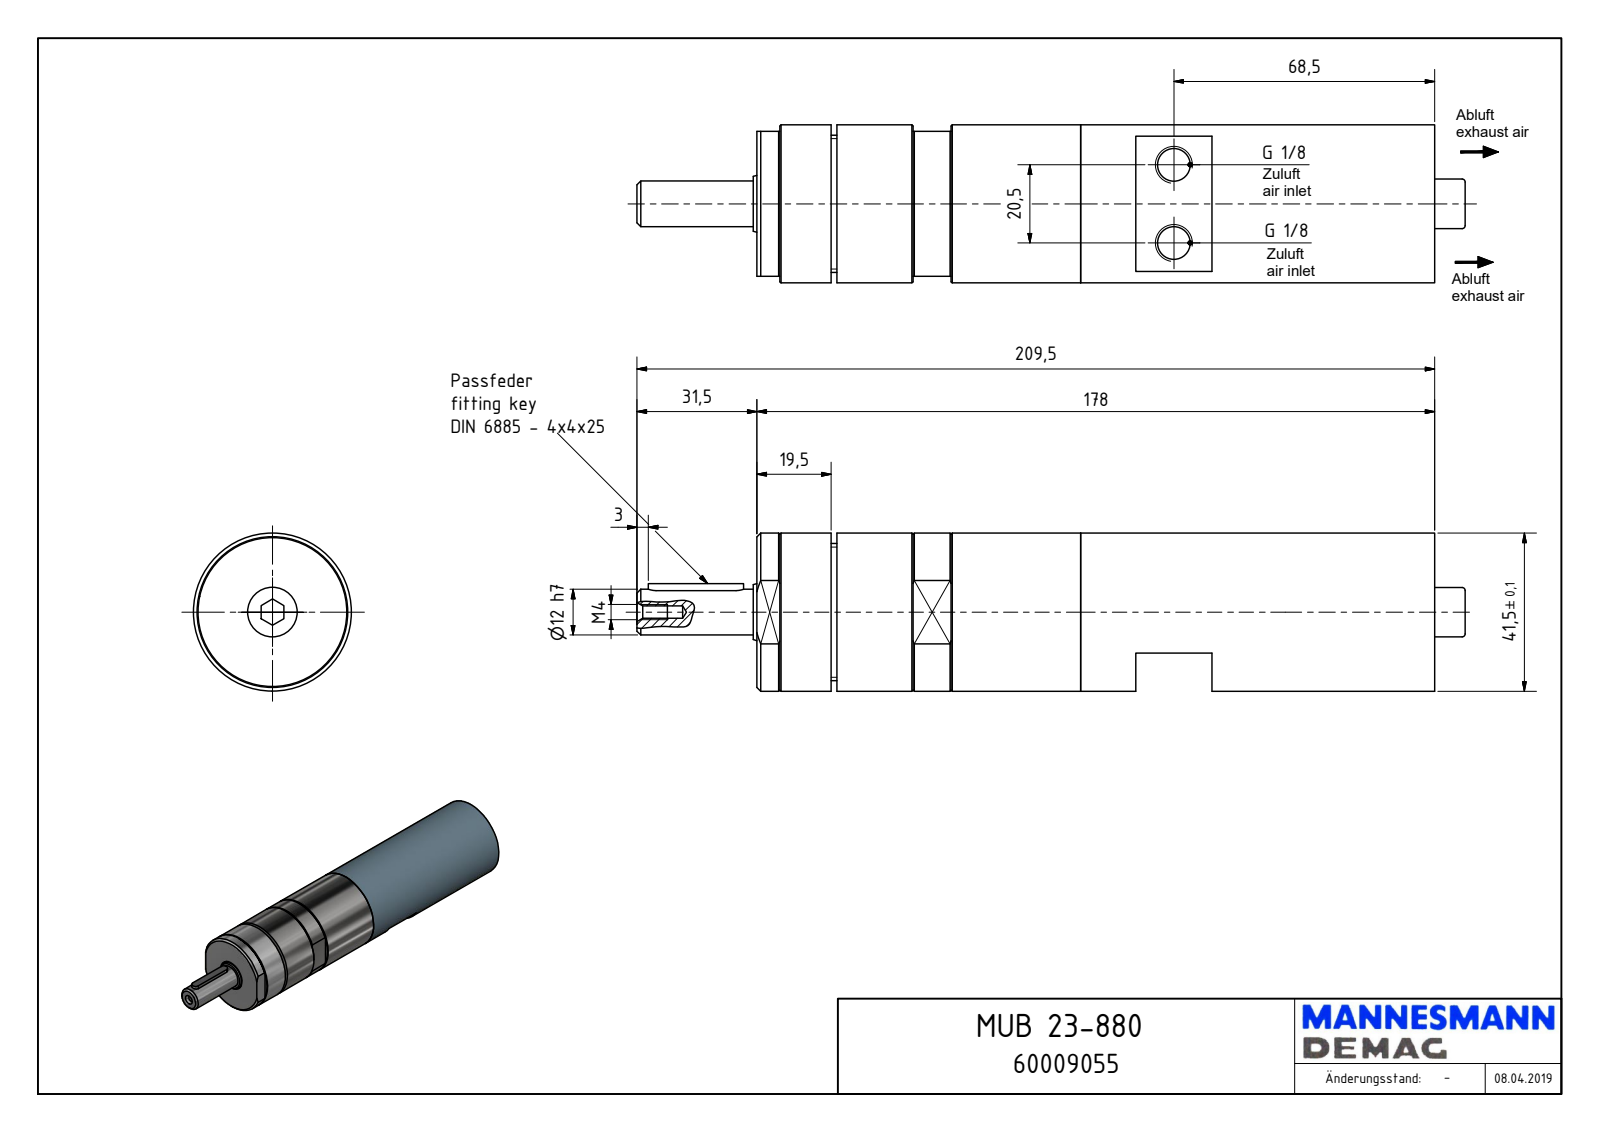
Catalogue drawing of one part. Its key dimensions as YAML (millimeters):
part_name: "MUB 23-880_60009055"
step_written_by: "Autodesk Inventor 2018 (AUTOMOTIVE_DESIGN)"
units: millimeters
bodies: {solids: 1, faces: 114, planar: 56, cylindrical: 41, other: 17}
overall_size: [217.5, 41.5, 41.5]
volume: 237746
surface_area: 33207
round_holes:
  - {diameter: 8.57, count: 2}
  - {diameter: 3.24, count: 1}
  - {diameter: 8.5, count: 1}
  - {diameter: 16, count: 1}
  - {diameter: 37, count: 1}
  - {diameter: 38.01, count: 1}
  - {diameter: 39.5, count: 1}
round_bosses_or_shafts:
  - {diameter: 41.5, count: 1}
  - {diameter: 39.17, count: 1}
  - {diameter: 39, count: 1}
  - {diameter: 36, count: 1}
  - {diameter: 27.91, count: 1}
  - {diameter: 14.95, count: 1}
  - {diameter: 13, count: 1}
  - {diameter: 12, count: 1}
partial_cylinders:
  - {radius: 2, count: 4}
  - {radius: 2.5, count: 2}
face_to_face_distances: [178, 82, 78.5, 95.95, 82.05, 96, 3.5, 23.5, 55, 123.31]
hole_center_spacings: [20.5]
